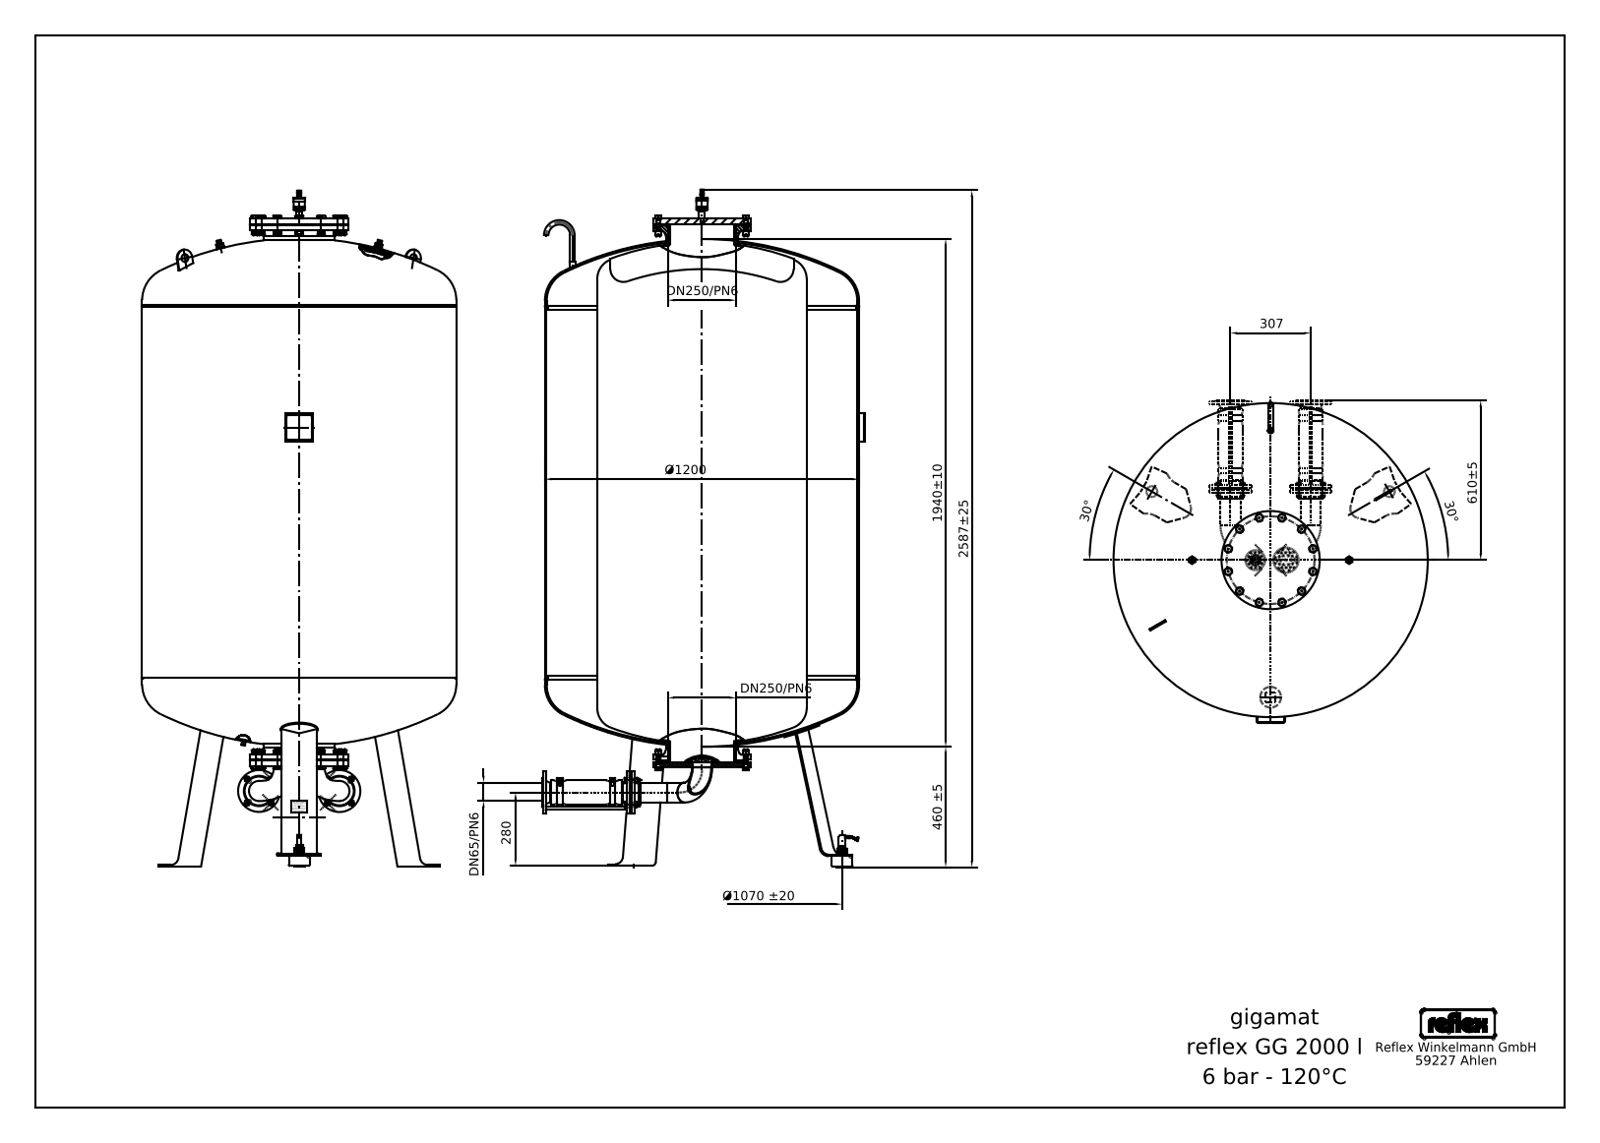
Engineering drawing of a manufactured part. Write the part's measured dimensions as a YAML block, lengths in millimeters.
step_written_by: "Mechanical Desktop 2008 (CONFIG_CONTROL_DESIGN)"
units: millimeters
bodies: {solids: 24, faces: 1074, planar: 569, cylindrical: 268, other: 237}
overall_size: [2587, 1208.35, 1200]
volume: 2035000000
surface_area: 15490000
round_holes:
  - {diameter: 14, count: 8}
  - {diameter: 8, count: 1}
  - {diameter: 30, count: 1}
  - {diameter: 70.3, count: 1}
  - {diameter: 76.1, count: 1}
  - {diameter: 260.4, count: 1}
round_bosses_or_shafts:
  - {diameter: 16, count: 24}
  - {diameter: 160, count: 2}
  - {diameter: 96.1, count: 2}
  - {diameter: 86.1, count: 2}
  - {diameter: 76.1, count: 2}
  - {diameter: 16.6, count: 2}
  - {diameter: 12, count: 2}
  - {diameter: 10, count: 2}
partial_cylinders:
  - {radius: 25, count: 18}
  - {radius: 2, count: 8}
  - {radius: 8.44, count: 4}
  - {radius: 3.38, count: 3}
  - {radius: 5.76, count: 2}
  - {radius: 9, count: 2}
  - {radius: 10.12, count: 2}
  - {radius: 13.91, count: 2}
face_to_face_distances: [1430, 22, 335, 1765, 2051, 27, 313, 1743, 2078, 2100]
hole_center_spacings: [65, 91.92, 307, 129.99, 265.06, 320.47, 355.94, 175.78]
